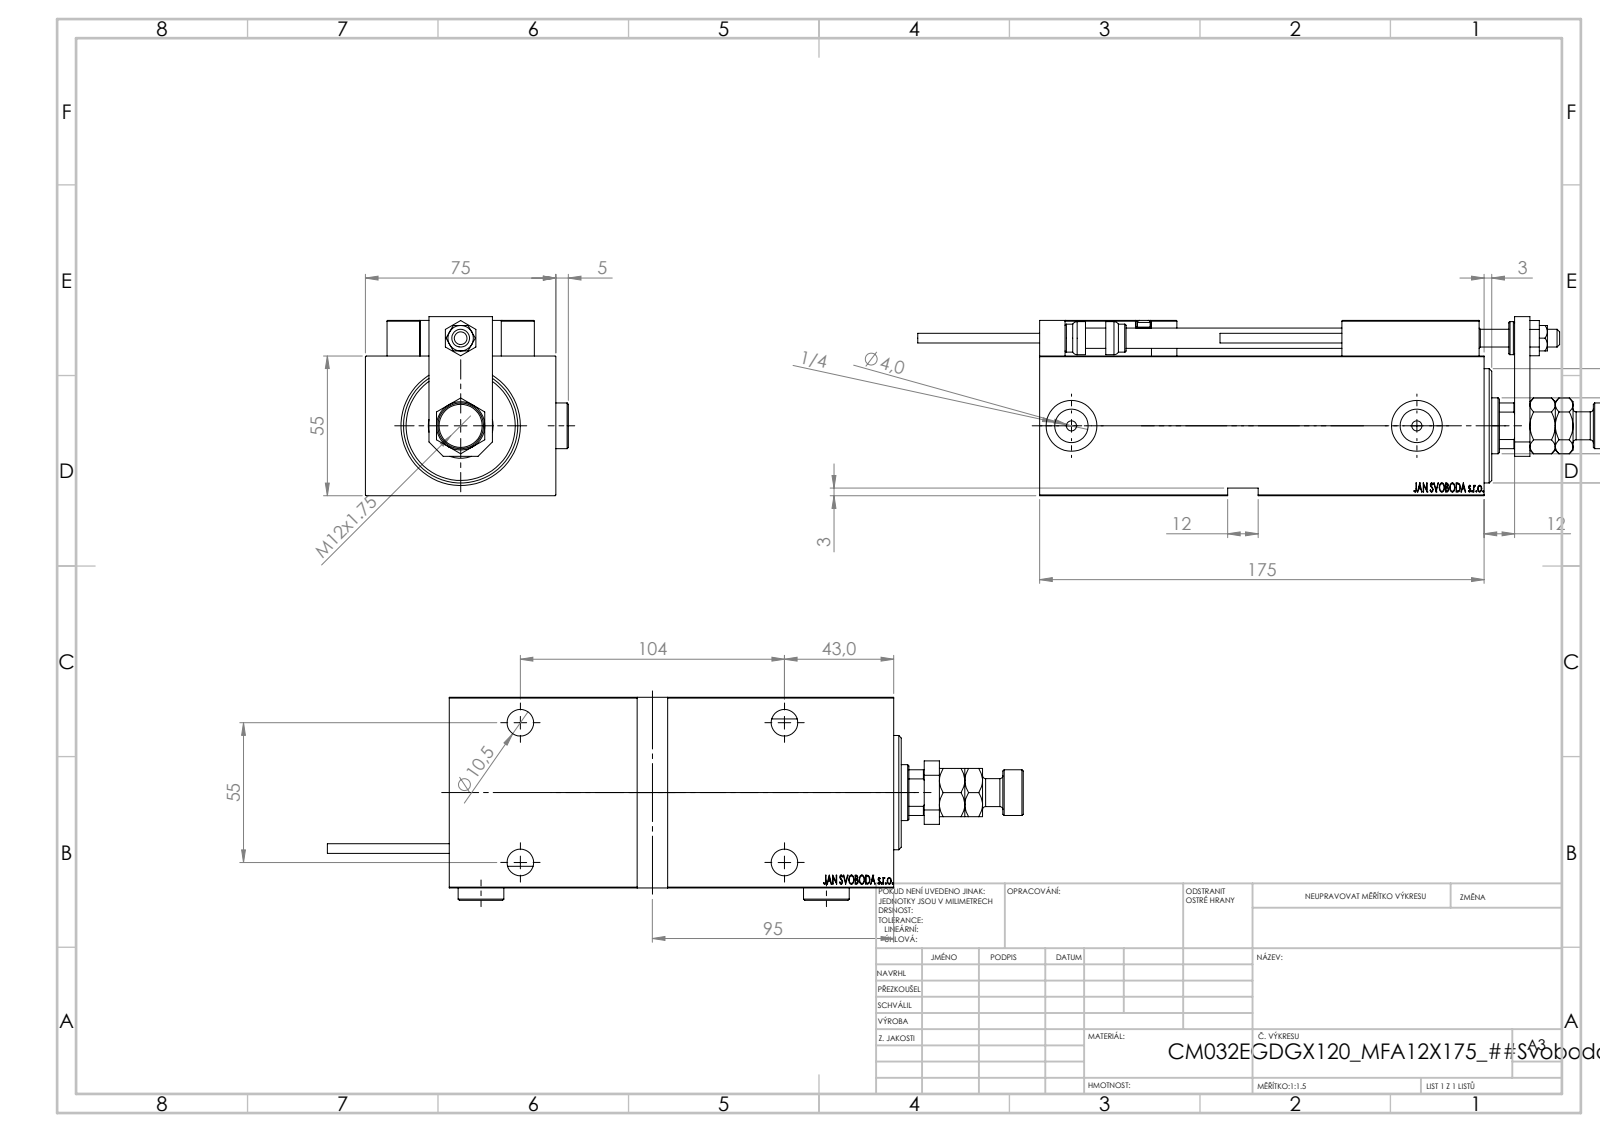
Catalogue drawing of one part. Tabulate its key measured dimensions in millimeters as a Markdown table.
| quantity | value |
| --- | --- |
| part name | KONCOVKA; NUT_D10; V450CM_E_Body; ALLEN BOLT D5 (+7 more) |
| STEP written by | SolidWorks 2019 (CONFIG_CONTROL_DESIGN) |
| units | millimeters |
| bodies | 27 solids, 1398 faces (621 planar, 200 cylindrical, 577 other) |
| overall size | 274 × 79.9 × 70.5 |
| volume | 705 494 mm³ |
| surface area | 133 915 mm² |
| round holes (diameter × count) | 4 × 6, 8 × 5, 10.5 × 5, 16.5 × 5, 3.2 × 4, 5 × 2, 13.16 × 2, 20 × 2, 7 × 1, 22 × 1, 25.5 × 1, 32 × 1 |
| round bosses / shafts (diameter × count) | 18 × 3, 11 × 2, 5 × 2, 3.8 × 2, 34 × 1, 13 × 1 |
| partial cylindrical surfaces (radius × count) | 0.3 × 30, 3 × 2, 10.5 × 1 |
| main face-to-face distances | 55, 75, 3, 10, 14, 12, 175, 5, 69, 165 |
| hole center spacings | 11.37, 20, 28.9, 29.59, 29.69, 36.06, 40.03, 42.19 |
